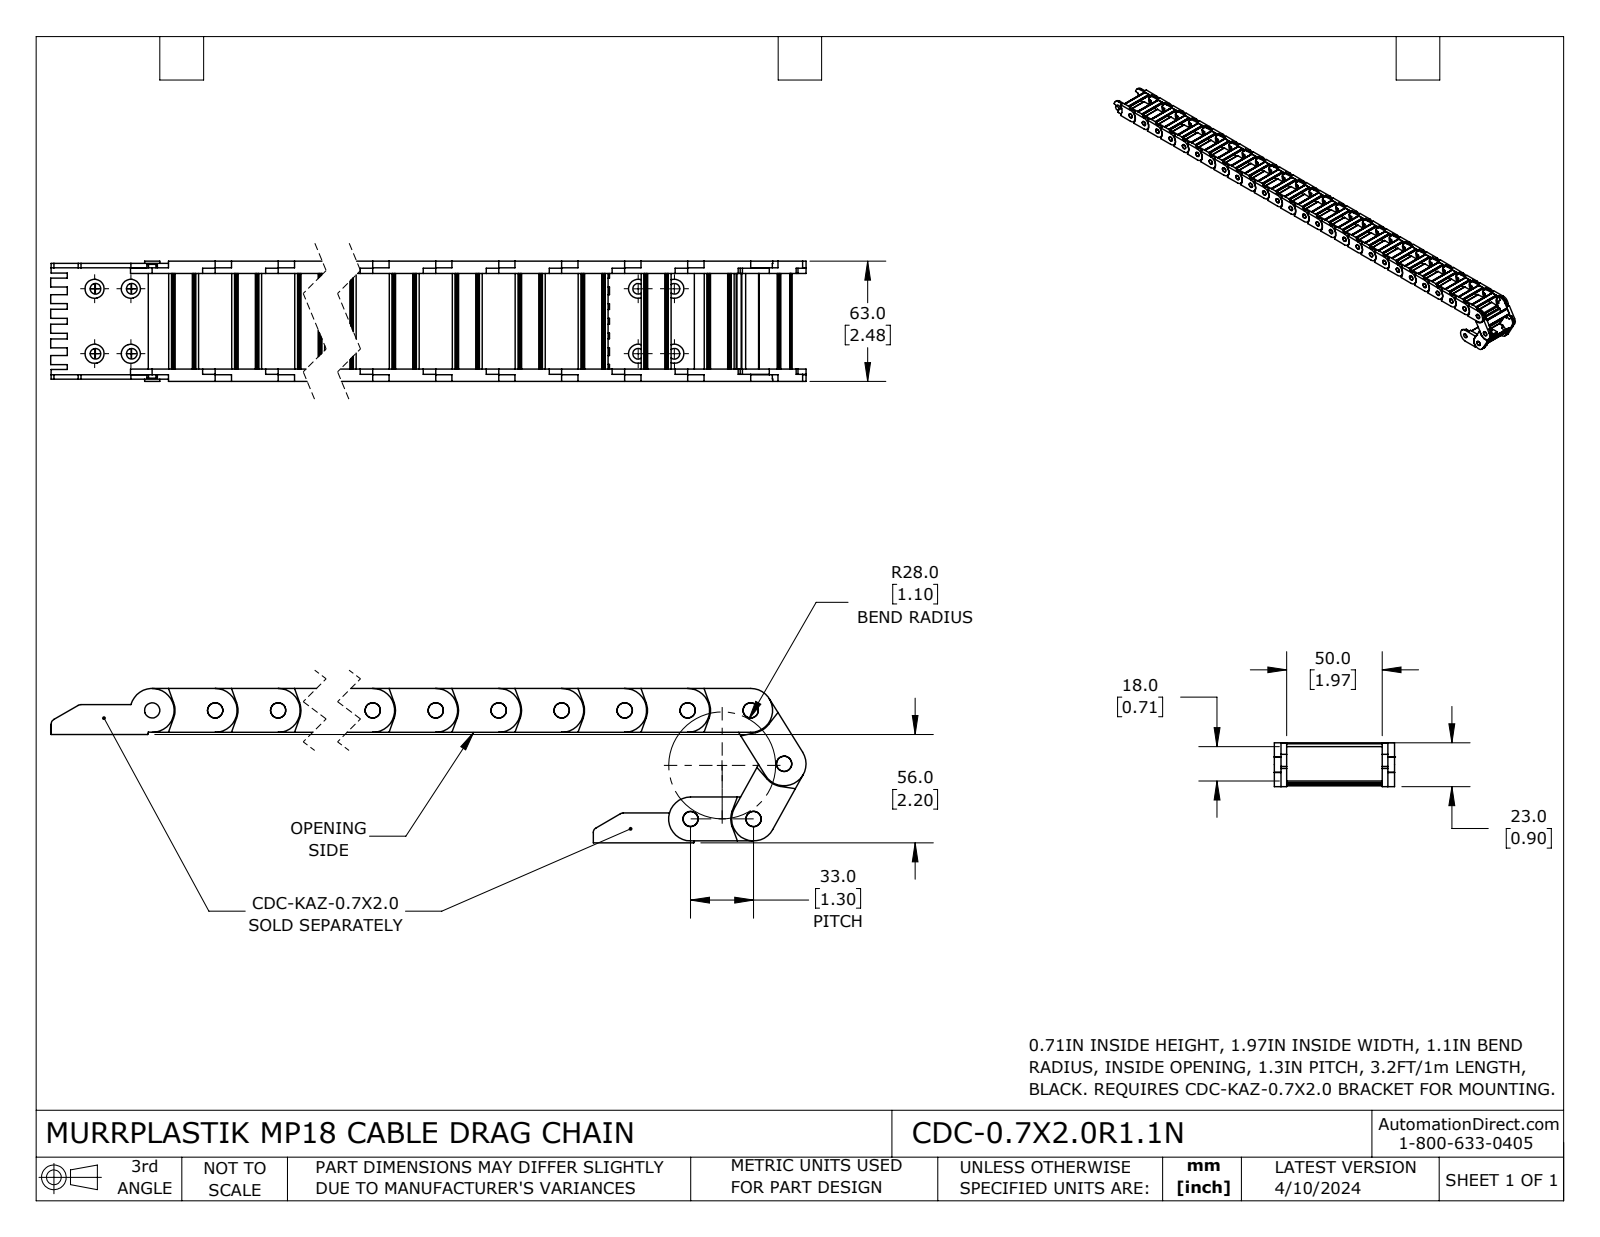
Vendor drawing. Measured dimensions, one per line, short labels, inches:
name: CDC-0.7X2.0R1.1N
written by: SolidWorks 2023 (CONFIG_CONTROL_DESIGN)
unit: in
bodies: 30 solids, 2370 faces (1110 planar, 1260 cylindrical, 0 other)
size: 36.667 × 3.143 × 2.48
volume: 21.06 in³; area: 414.1 in²
holes: 30× ⌀0.315
bosses: 1× ⌀0.315
rounds: 120× R0.02, 120× R0.059, 60× R0.008, 60× R0.012, 31× R0.453, 31× R0.47, 30× R0.197, 30× R0.215
face distances: 0.256, 2.224, 2.48, 0.138, 2.343, 0.118, 2.087, 0.079, 0.146, 2.335
hole spacings: 1.299, 2.598, 3.898, 5.197, 6.496, 7.795, 9.094, 10.394
